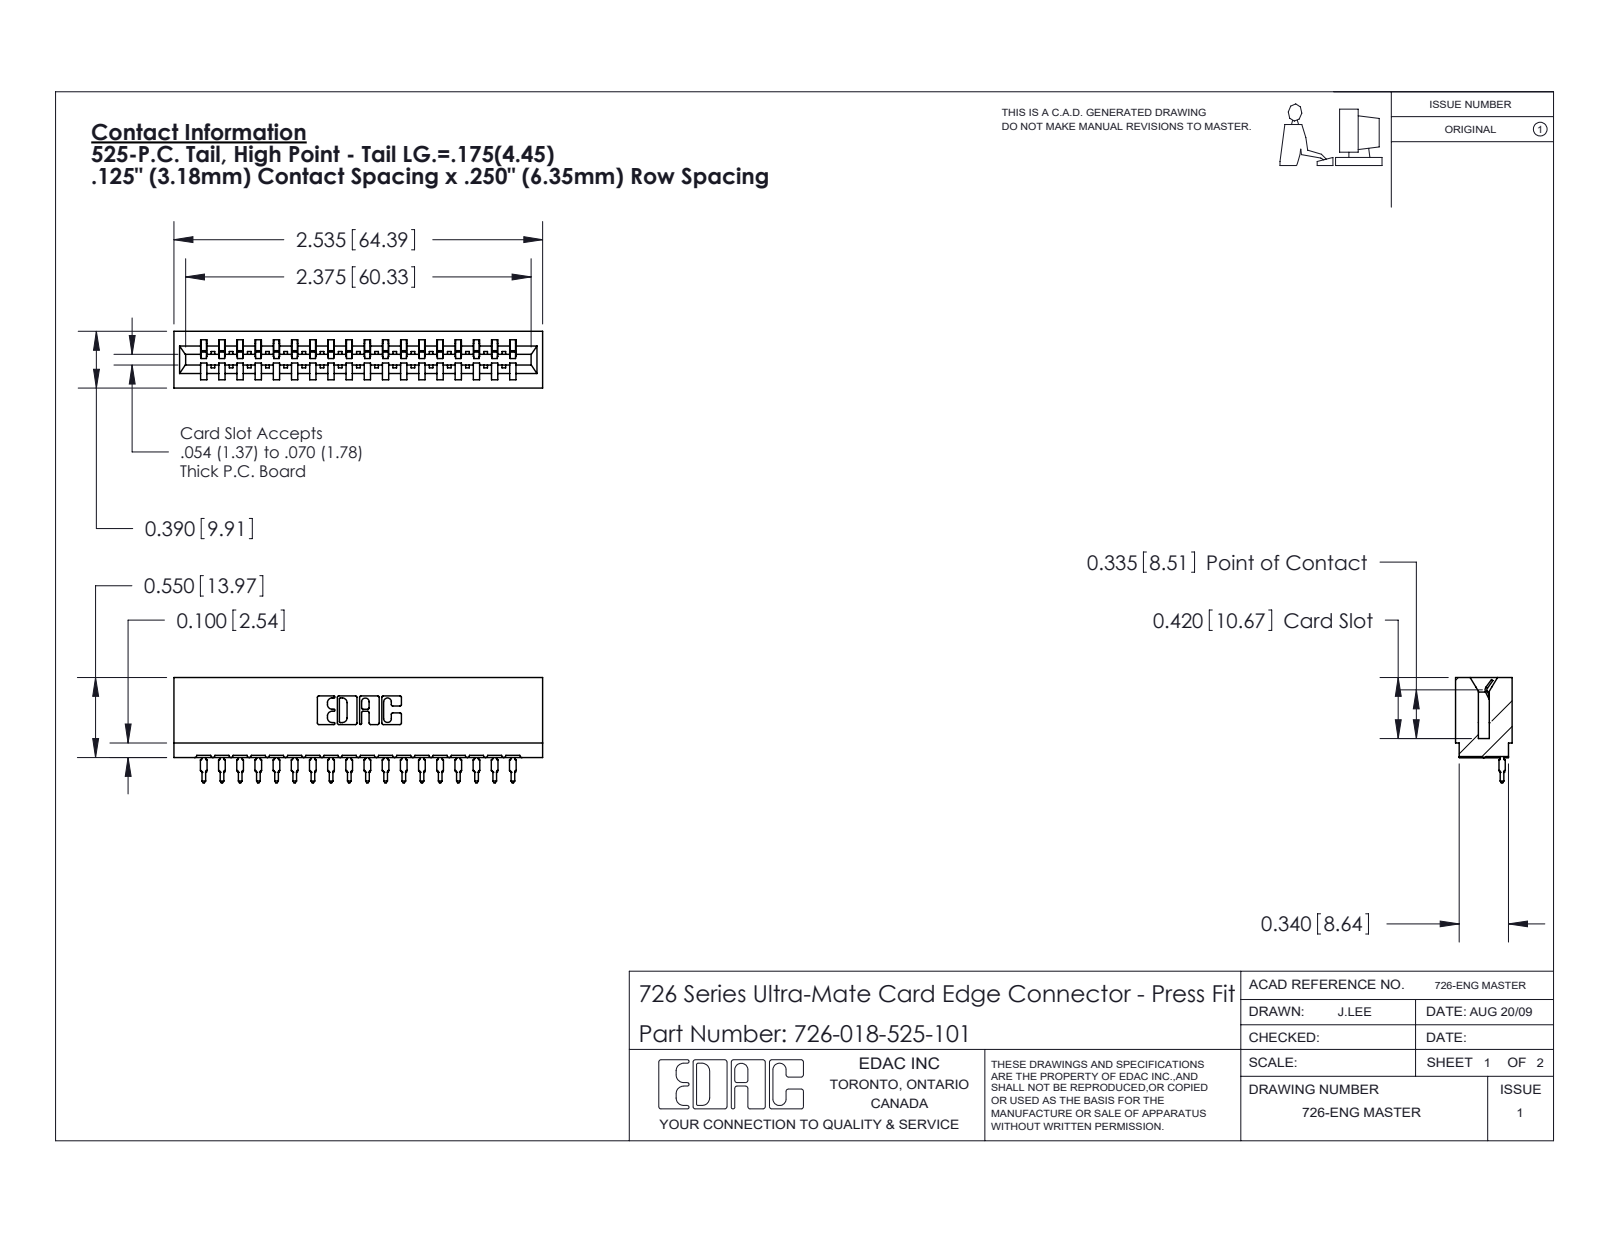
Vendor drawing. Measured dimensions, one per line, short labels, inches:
name: 726 Part_.515 Slot Depth - 01; 746-292-001_525; 726-018-525-101
written by: SolidWorks 2020 (CONFIG_CONTROL_DESIGN)
unit: in
bodies: 19 solids, 2041 faces (1189 planar, 384 cylindrical, 468 other)
size: 2.535 × 0.724 × 0.39
volume: 0.358 in³; area: 13.19 in²
rounds: 36× R0.021, 22× R0.01, 19× R0.015, 6× R0.007, 6× R0.031, 4× R0.005, 4× R0.011, 3× R0.026
face distances: 0.057, 0.333, 0.39, 0.25, 0.025, 0.307, 0.75, 0.5, 0.125, 0.083
